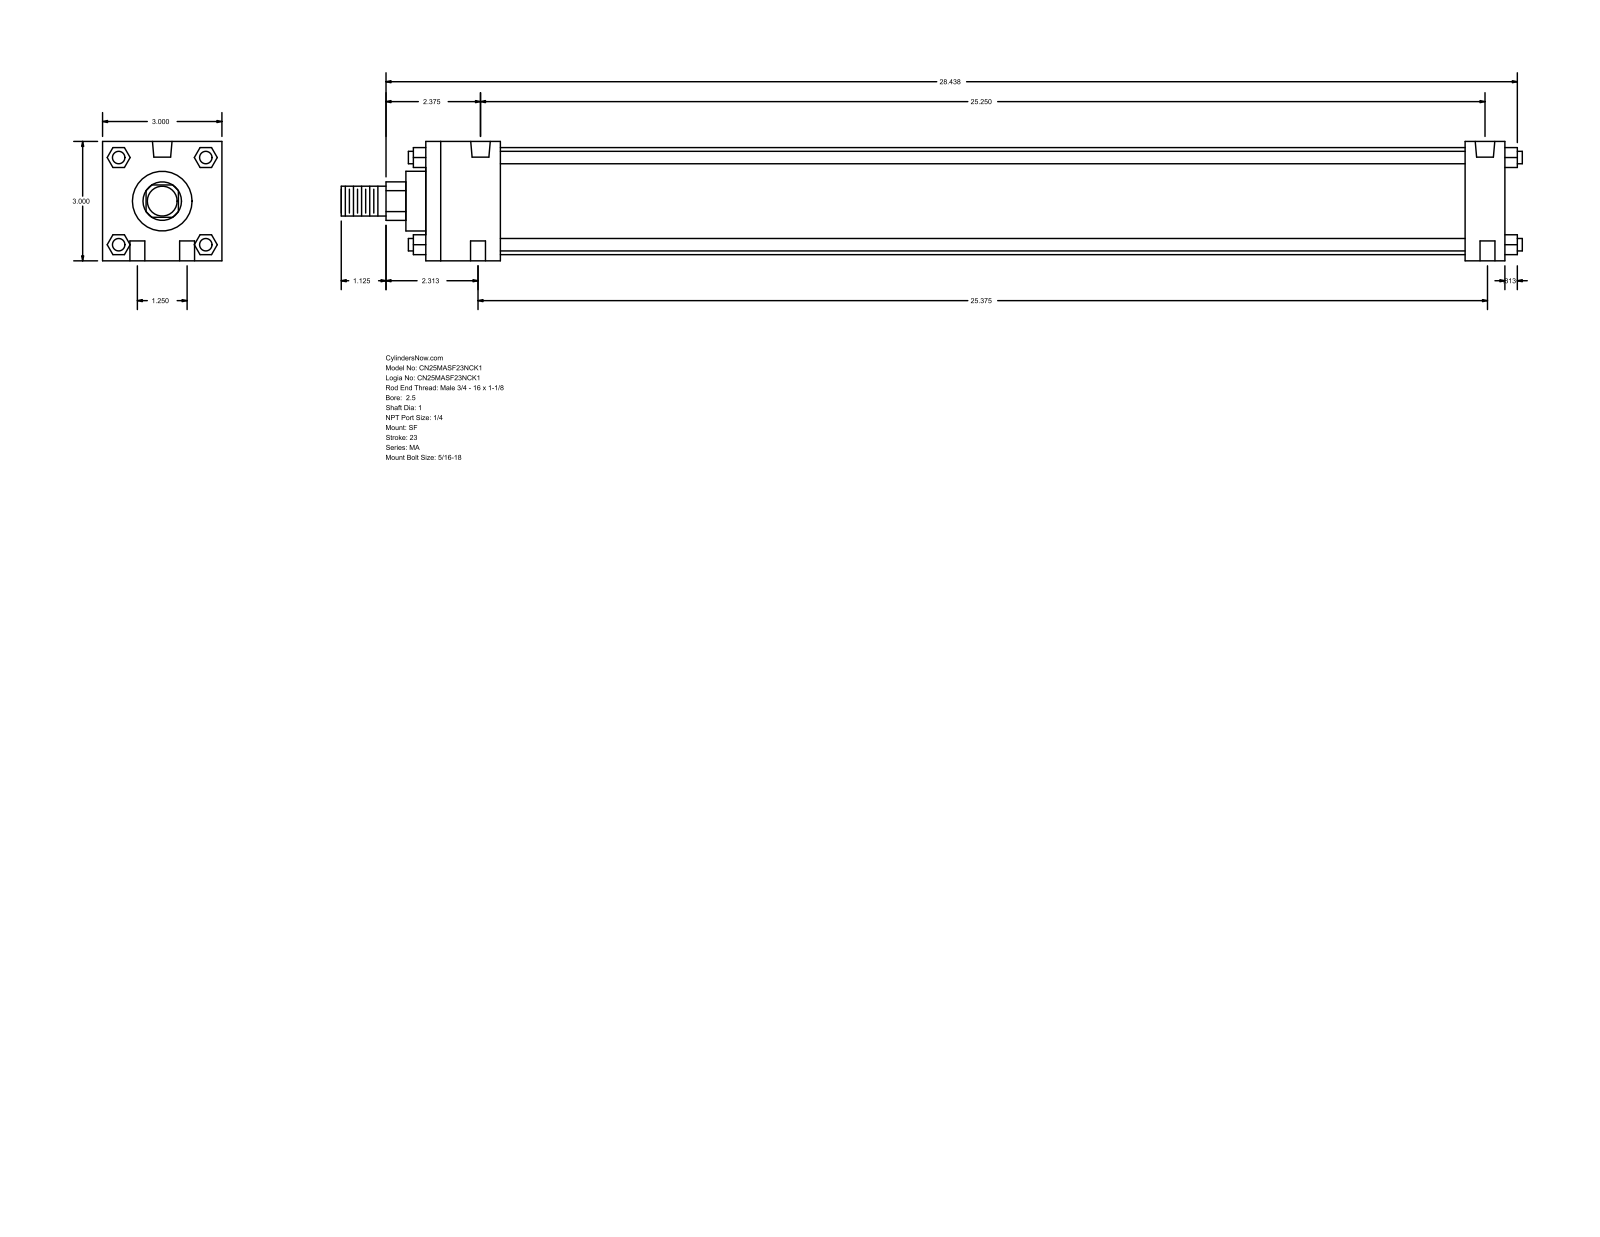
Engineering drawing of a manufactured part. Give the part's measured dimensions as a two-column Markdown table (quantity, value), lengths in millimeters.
| quantity | value |
| --- | --- |
| part name | MA_SF__0250_1 |
| STEP written by | GSSL Pune (CONFIG_CONTROL_DESIGN) |
| units | millimeters |
| bodies | 0 solids, 124 faces (94 planar, 30 cylindrical, 0 other) |
| overall size | 754.06 × 76.2 × 76.2 |
| round holes (diameter × count) | 9.53 × 4, 7.94 × 2, 12.49 × 2 |
| round bosses / shafts (diameter × count) | 7.94 × 4, 68.33 × 1, 38.1 × 1, 25.4 × 1, 19.05 × 1 |
| partial cylindrical surfaces (radius × count) | 12.29 × 1 |
| main face-to-face distances | 76.2, 688.98, 12.7, 25.4, 663.58, 47.63, 615.95, 641.35, 27.81, 48.17 |
| hole center spacings | 15.96, 643.13, 31.76, 641.34, 644.52, 645.3 |
